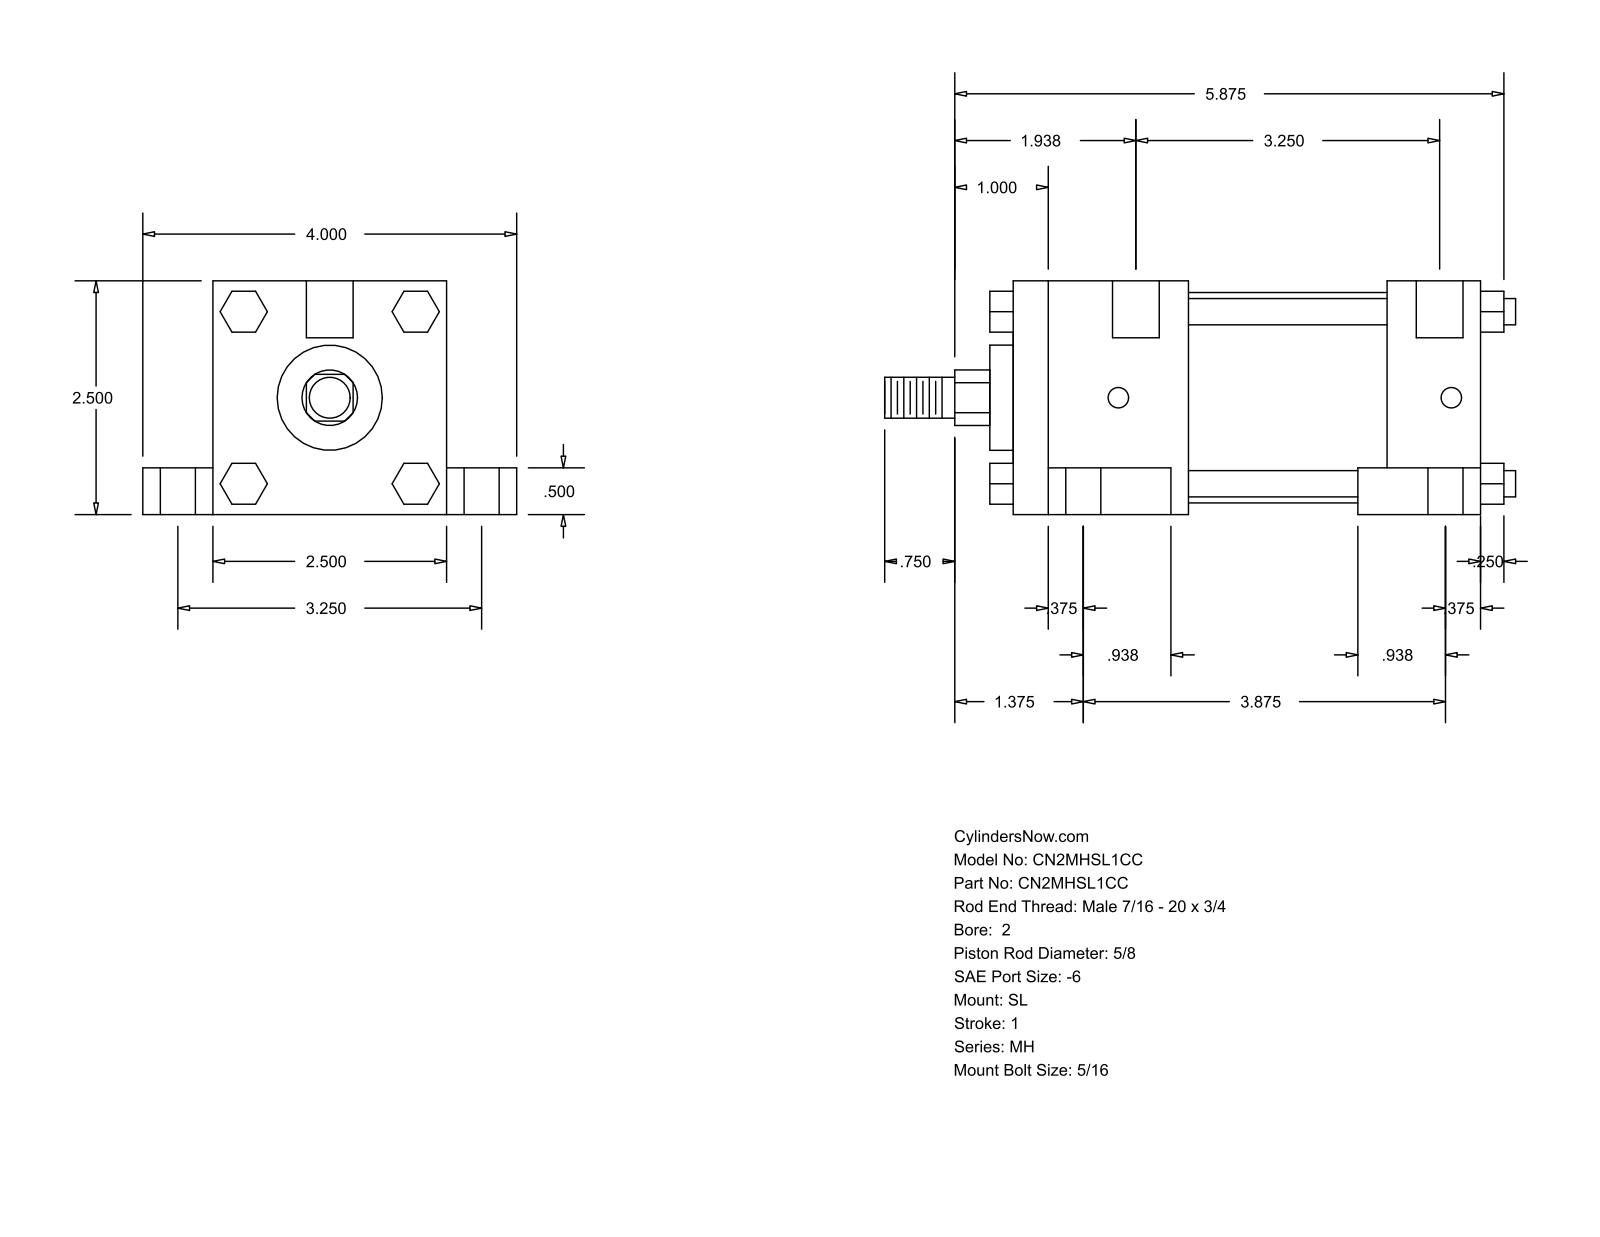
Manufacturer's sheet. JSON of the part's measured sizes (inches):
{"part_name": "MH_SL__0200_0.625", "step_written_by": "GSSL Pune (CONFIG_CONTROL_DESIGN)", "units": "inches", "bodies": {"solids": 0, "faces": 148, "planar": 112, "cylindrical": 36, "other": 0}, "overall_size": [6.75, 4, 2.5], "round_holes": [[0.219, 4], [0.375, 4], [0.625, 4], [0.5, 2]], "round_bosses_or_shafts": [[0.281, 4], [2.25, 1], [1.125, 1], [0.625, 1], [0.437, 1]], "partial_cylinders_radius": [[0.297, 1]], "face_to_face_distances": [2.5, 5, 2, 2.125, 0.5, 0.75, 3.25, 4, 1, 1.875], "hole_center_spacings": [1.626, 1.668, 1.719, 3.25, 3.563, 3.69, 3.859, 3.875]}
